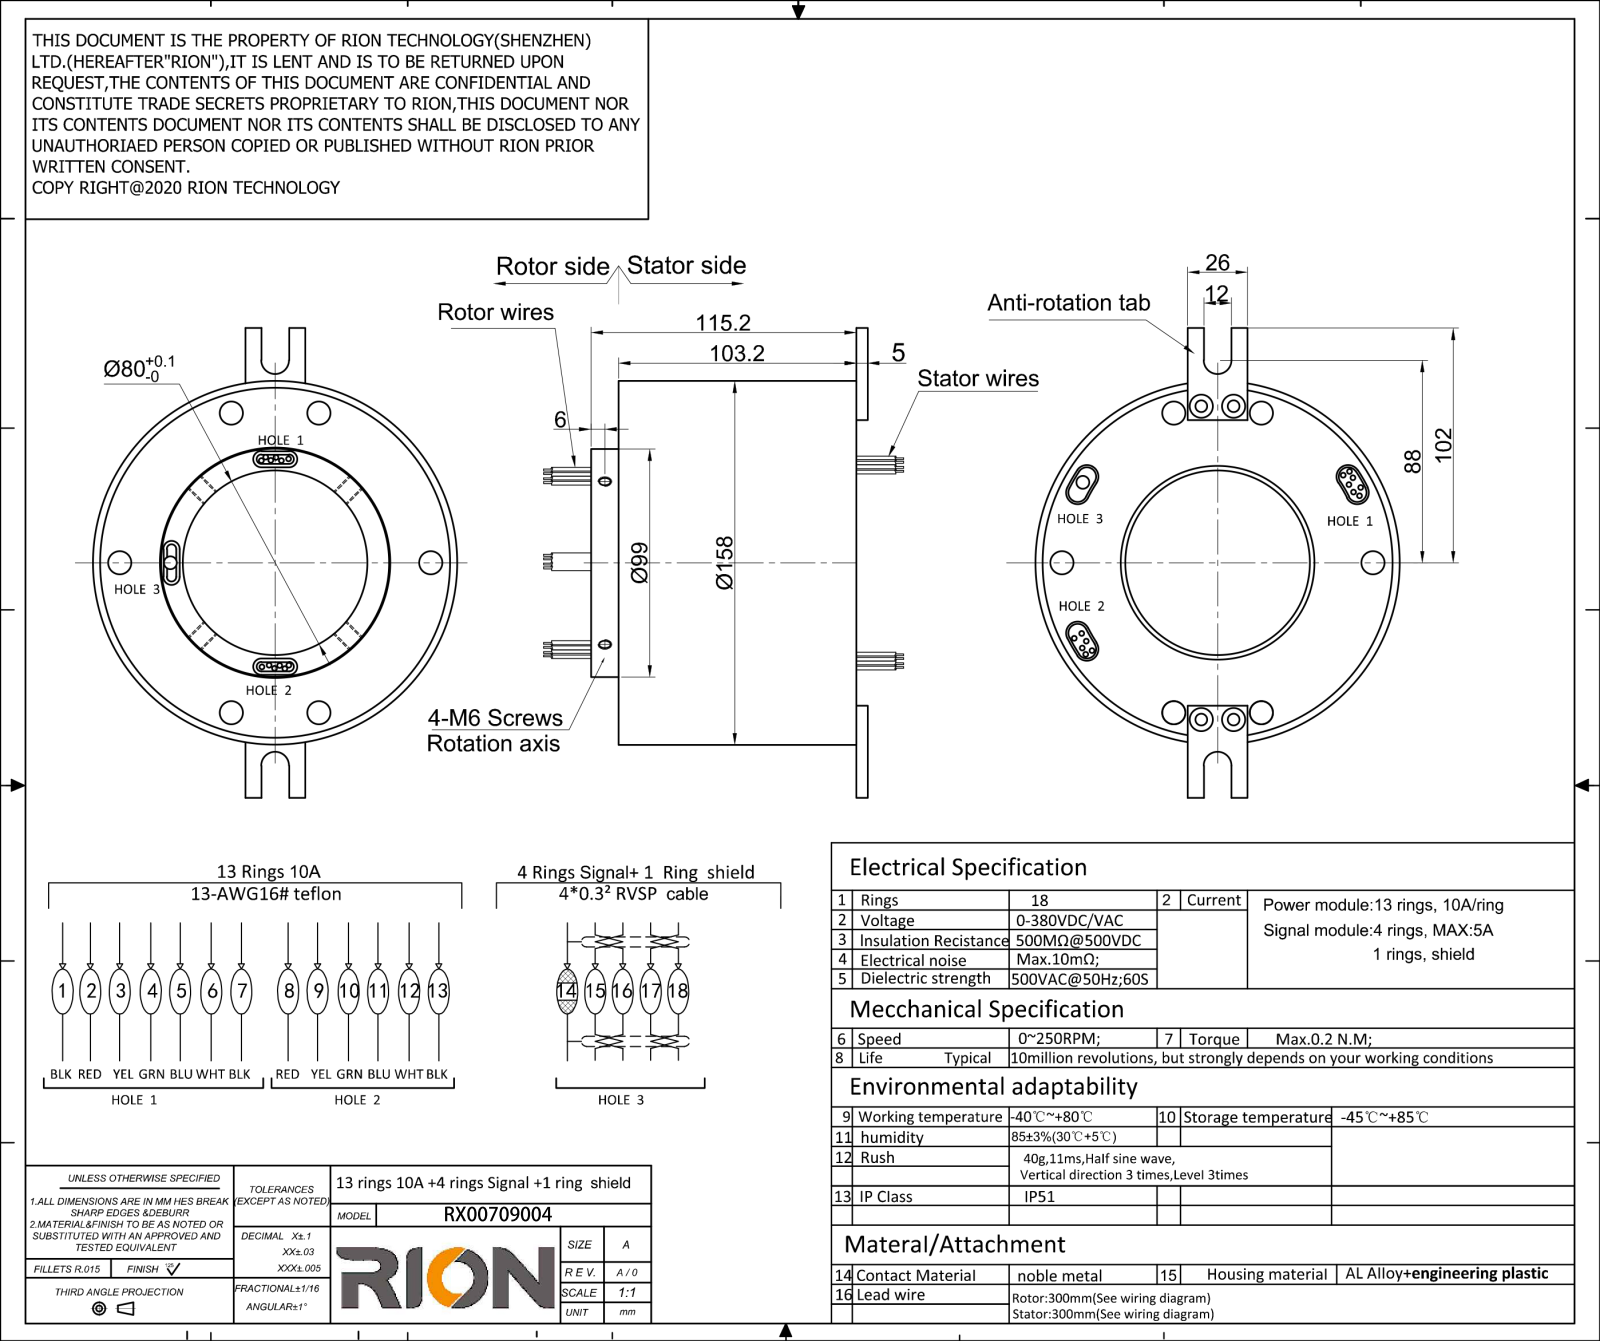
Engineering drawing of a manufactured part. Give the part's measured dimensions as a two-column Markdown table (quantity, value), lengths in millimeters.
| quantity | value |
| --- | --- |
| part name | MT80158-P1310-S05 |
| STEP written by | SolidWorks 2014 (CONFIG_CONTROL_DESIGN) |
| units | millimeters |
| bodies | 1 solid, 216 faces (83 planar, 117 cylindrical, 16 other) |
| overall size | 204 × 183.2 × 158 |
| volume | 1 547 000 mm³ |
| surface area | 132 825 mm² |
| round holes (diameter × count) | 5 × 8, 4.2 × 4, 80 × 1, 94 × 1, 152 × 1 |
| round bosses / shafts (diameter × count) | 2.1 × 26, 5.6 × 2, 158 × 1, 151.8 × 1, 99 × 1, 93.8 × 1 |
| partial cylindrical surfaces (radius × count) | 2 × 6, 4 × 6, 6 × 2 |
| main face-to-face distances | 103.2, 12, 115.2, 5, 120.2, 108.2, 1, 26, 114.2, 7 |
| hole center spacings | 68.36, 14, 136, 136.72 |
